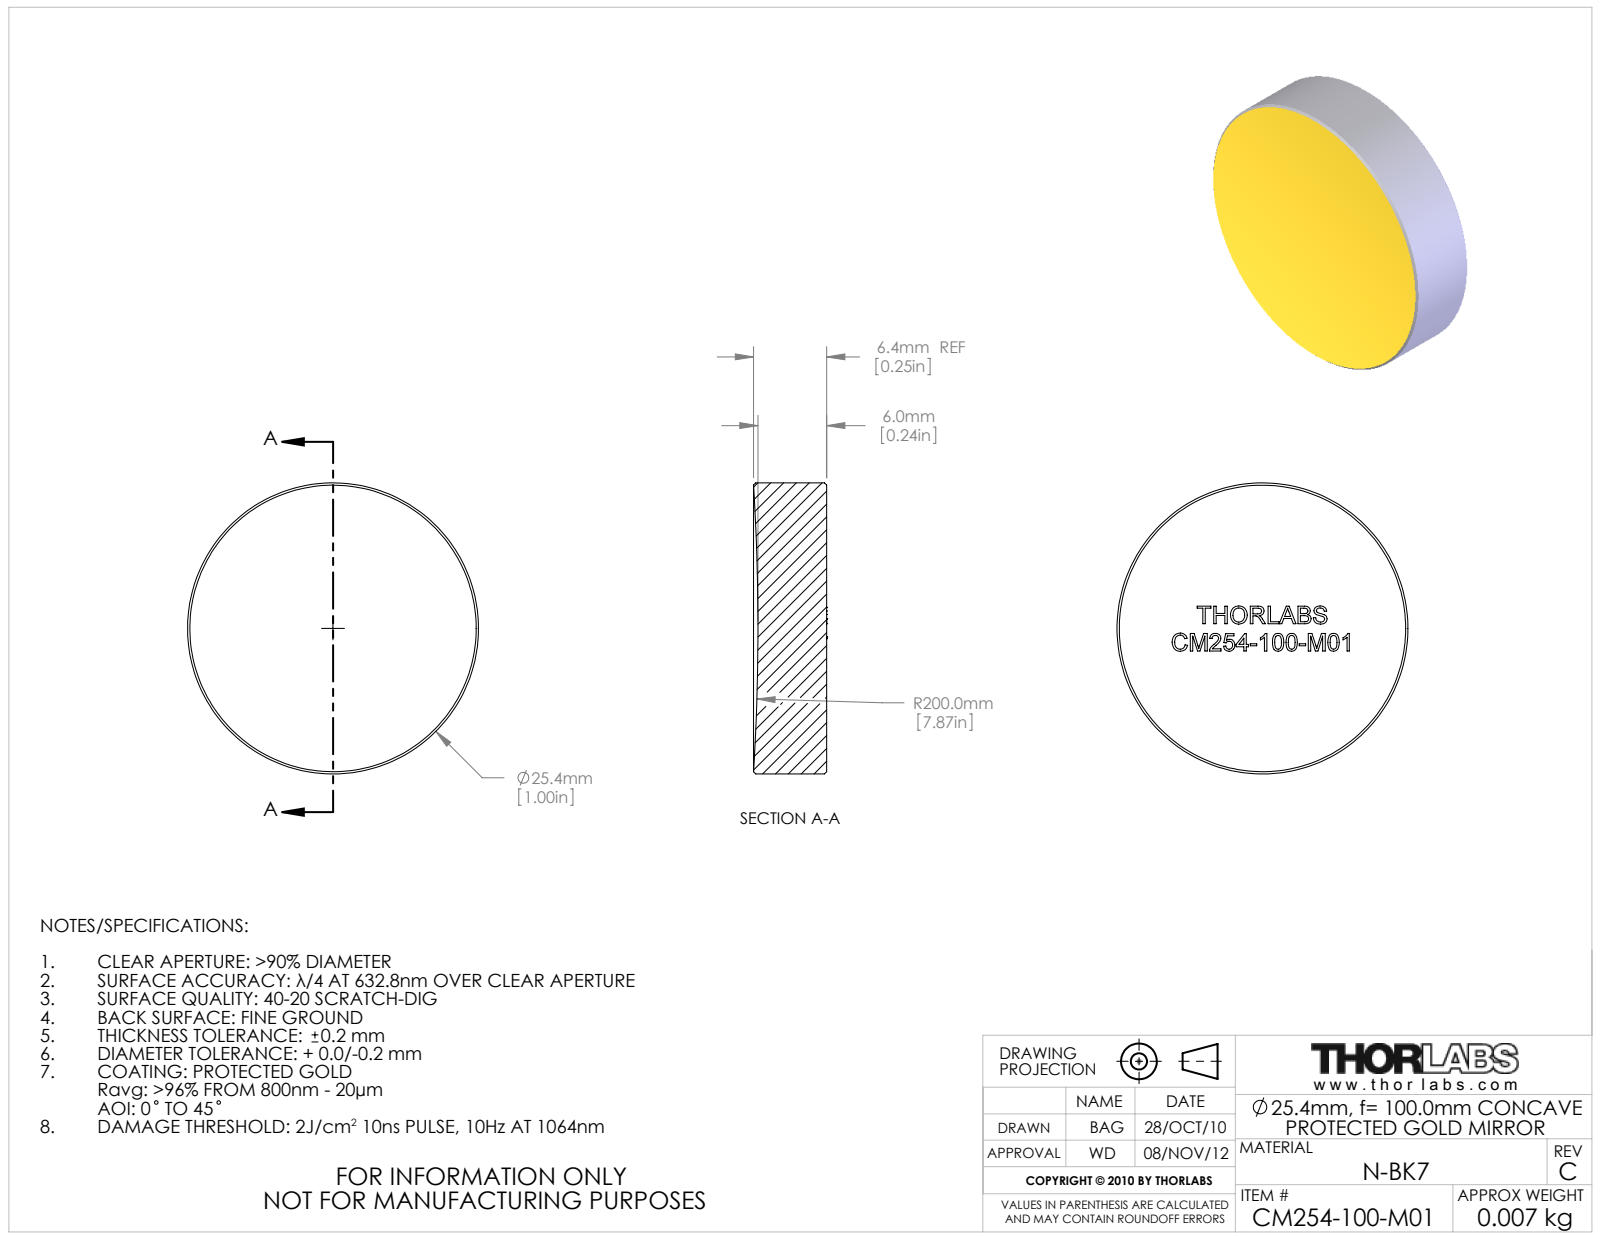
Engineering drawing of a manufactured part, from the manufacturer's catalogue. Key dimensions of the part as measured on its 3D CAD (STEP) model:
Part name (STEP PRODUCT): 17585-E0W
STEP written by: SolidWorks 2009 (AUTOMOTIVE_DESIGN)
Units: inches
Bodies: 1 solid, 275 faces (161 planar, 2 cylindrical, 112 other)
Overall size (bounding box): 1 × 1 × 0.252
Volume: 0.192 in³ · Surface area: 2.333 in²
Round bosses / shafts (diameter × count): ⌀1 ×1
Main face-to-face distances: 0.061, 0.076, 0.093, 0.037, 0.043, 0.058, 0.094, 0.038, 0.405, 0.129
